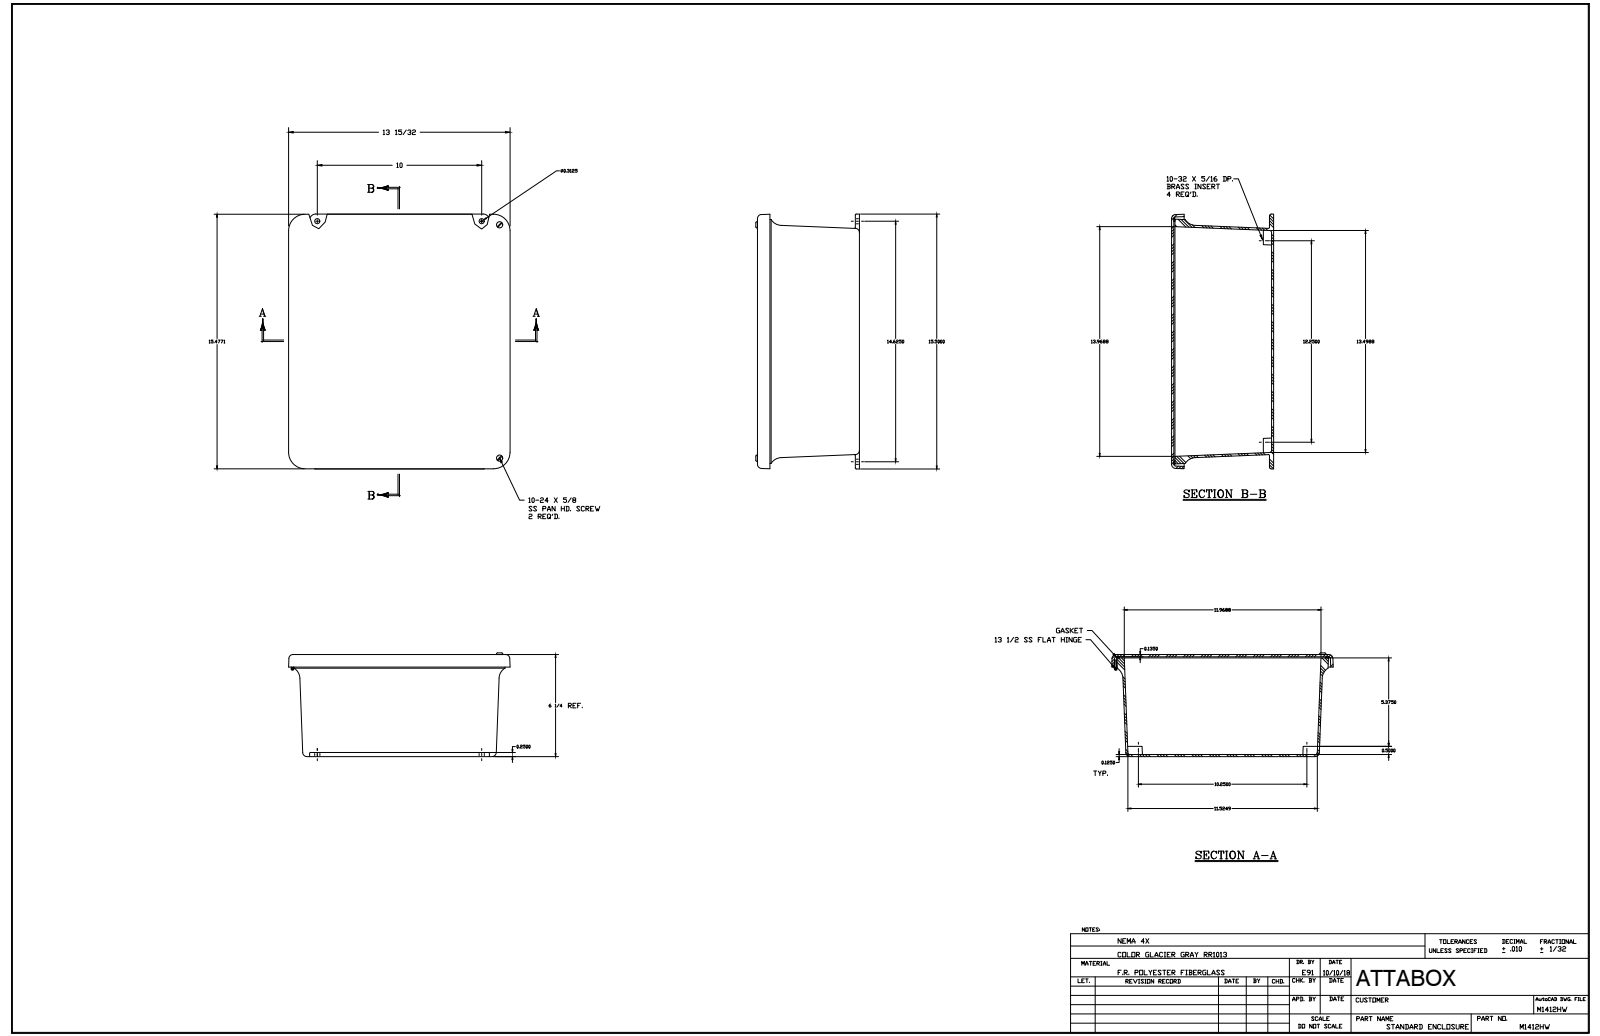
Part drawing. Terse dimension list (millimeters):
name: M1412HW
written by: SolidWorks 2018 (AUTOMOTIVE_DESIGN)
unit: mm
bodies: 24 solids, 866 faces (317 planar, 338 cylindrical, 211 other)
size: 393.7 × 343 × 161.1
volume: 1 852 000 mm³; area: 1 013 000 mm²
holes: 10× ⌀3.3, 10× ⌀3.6, 8× ⌀3.9, 4× ⌀4, 4× ⌀5.5, 2× ⌀3.7, 1× ⌀2.2
bosses: 10× ⌀6.4, 6× ⌀6.9, 5× ⌀3.2, 5× ⌀3.2, 2× ⌀4.8, 2× ⌀4, 1× ⌀3.9, 1× ⌀3.9
rounds: 20× R0.8, 12× R3.2, 12× R6.4, 6× R5.1, 4× R9.5, 4× R19.1, 2× R1.6
face distances: 3.2, 3.4, 154.4, 157.8, 151.2, 154.6, 3.2, 8.4, 3.9, 2
hole spacings: 82.6, 165.1, 247.7, 6.4, 76.2, 34.8, 158.8, 286
